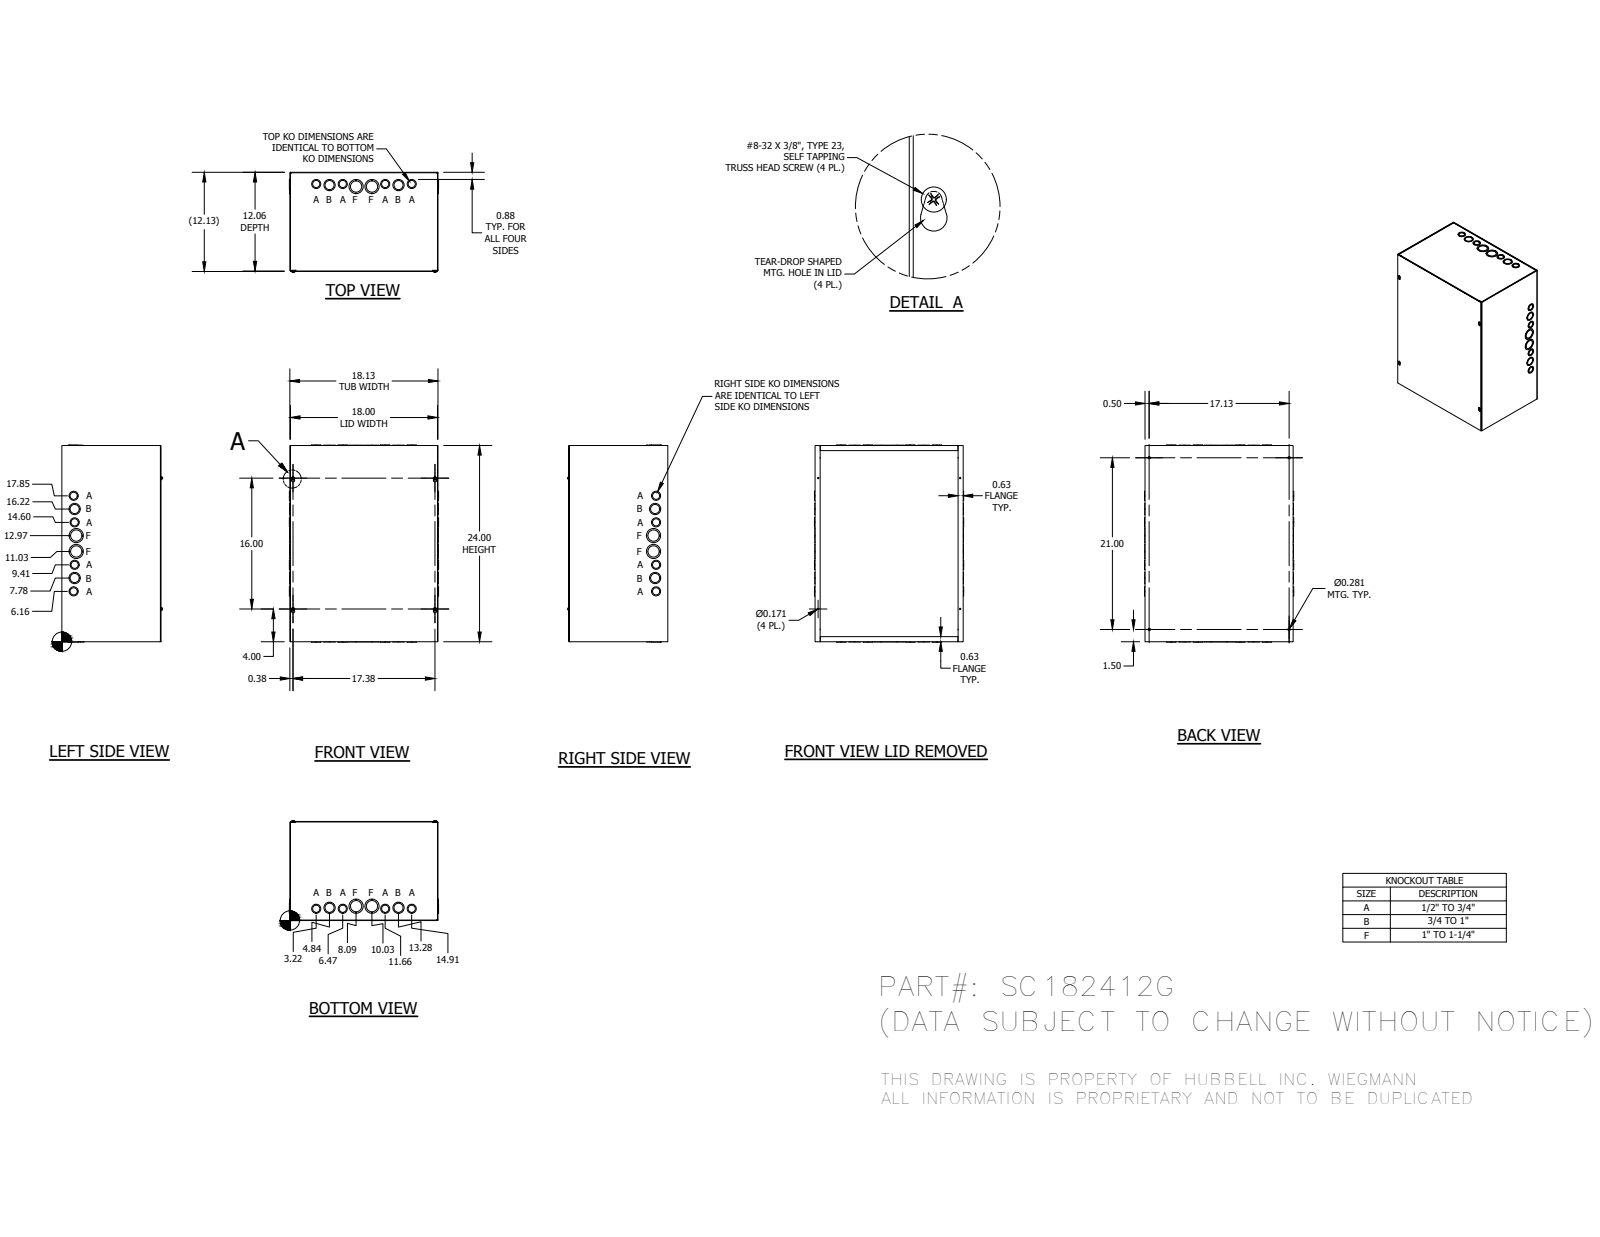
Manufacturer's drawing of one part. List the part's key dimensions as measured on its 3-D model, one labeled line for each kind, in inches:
Part name (STEP PRODUCT): SC182412GBLR; SC1812GTB; SC1824GLPA; 34056 (+1 more)
STEP written by: Autodesk Inventor 2014 (AUTOMOTIVE_DESIGN)
Units: inches
Bodies: 37 solids, 1167 faces (859 planar, 240 cylindrical, 68 other)
Overall size (bounding box): 24.125 × 18.25 × 12.225
Round holes (diameter × count): ⌀1.125 ×14, ⌀0.875 ×10, ⌀1.375 ×8, ⌀0.171 ×4, ⌀0.281 ×4, ⌀1.75 ×4
Round bosses / shafts (diameter × count): ⌀0.384 ×4, ⌀0.164 ×4
Partial cylindrical surfaces — rounded edges, fillets, slot ends (radius × count): R0.016 ×12, R0.078 ×12, R0.125 ×4, R0.203 ×4
Main face-to-face distances: 0.063, 12.063, 18.063, 12, 12.125, 23.937, 18, 18.125, 24, 23.875
Hole centre spacings: 1.63, 1.63, 1.655, 2.503, 3.25, 3.256, 3.579, 4.885
